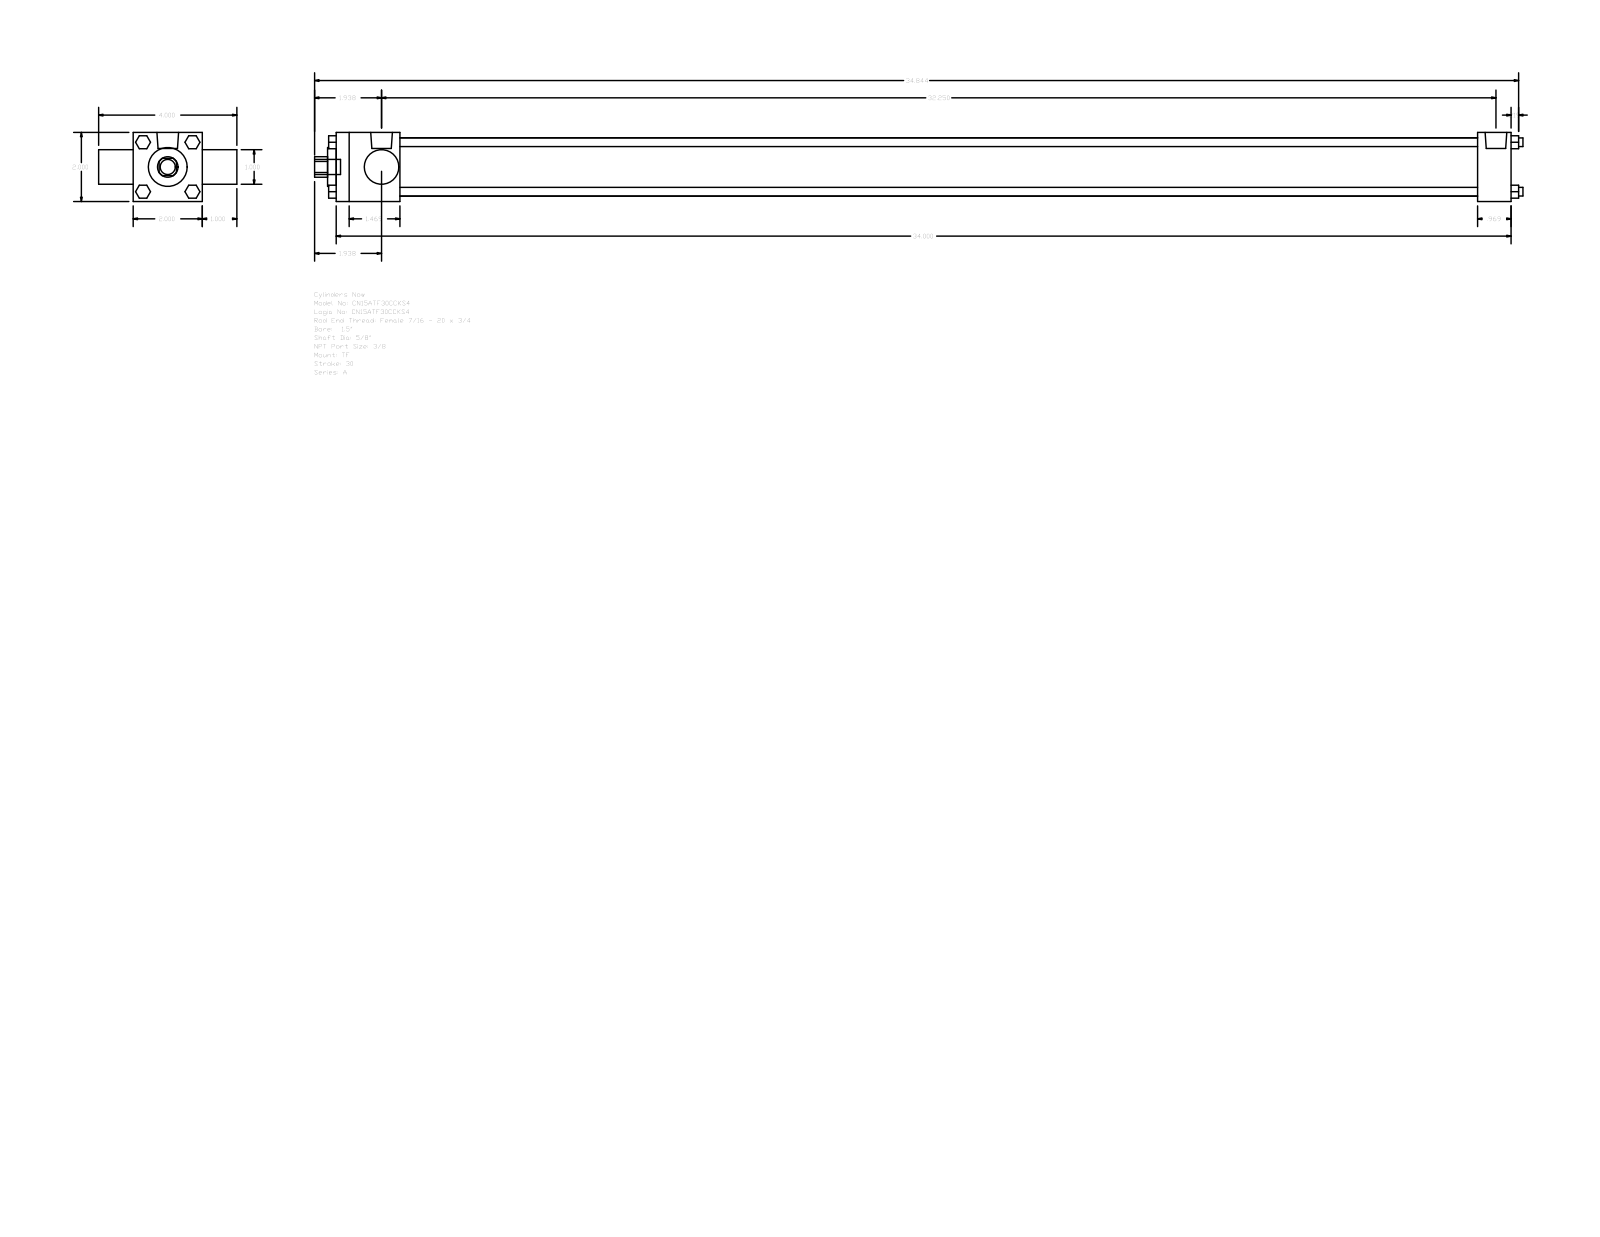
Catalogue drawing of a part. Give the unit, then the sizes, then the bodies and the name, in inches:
Units: inches
Overall size (bounding box): 34.969 × 4 × 2
Round holes (diameter × count): ⌀0.625 ×1, ⌀1 ×1, ⌀1.125 ×1, ⌀1.69 ×1
Round bosses / shafts (diameter × count): ⌀0.25 ×4, ⌀0.219 ×3, ⌀0.627 ×2, ⌀0.437 ×1
Partial cylindrical surfaces — rounded edges, fillets, slot ends (radius × count): R0.297 ×1
Main face-to-face distances: 2, 34, 1, 3, 1.844, 33.031, 31.187, 32.156, 0.969, 0.375
Bodies: 0 solids, 120 faces (92 planar, 28 cylindrical, 0 other)
Part name (STEP PRODUCT): A_TF__0150_0.625
STEP written by: GSSL Pune (CONFIG_CONTROL_DESIGN)
